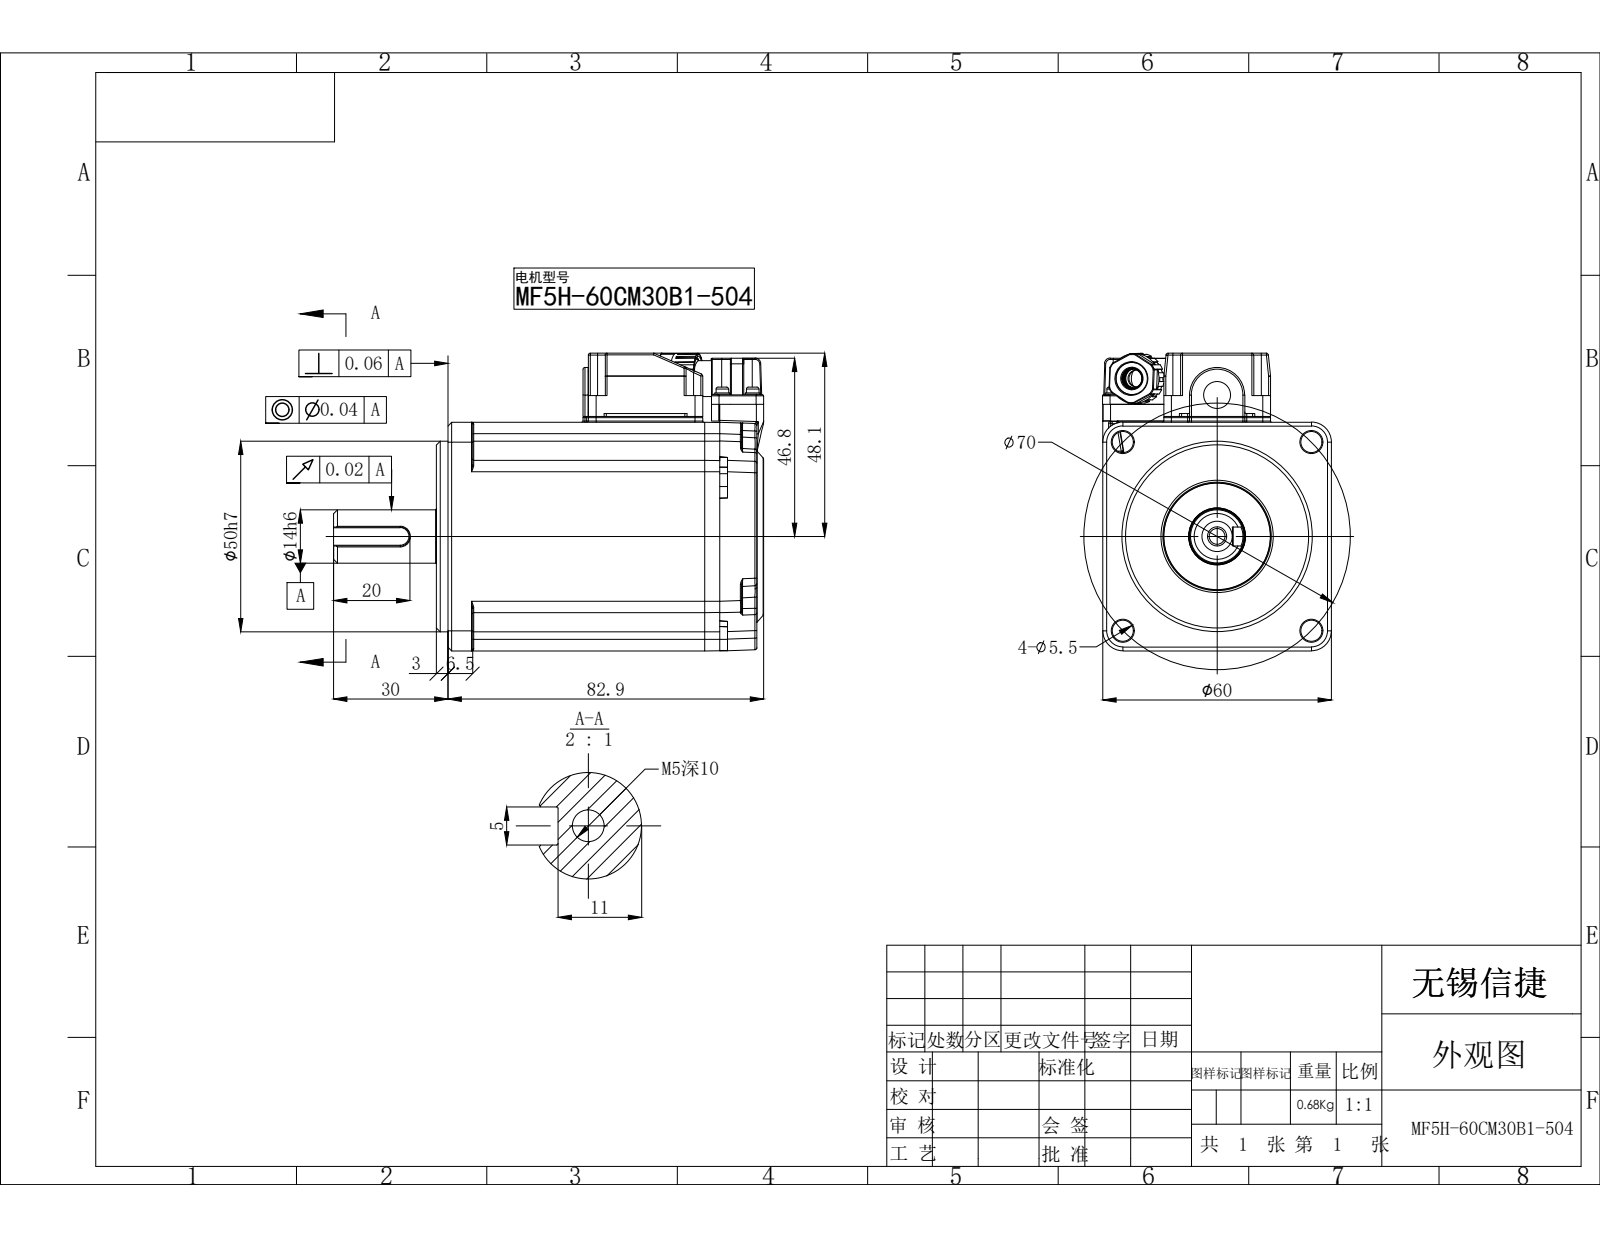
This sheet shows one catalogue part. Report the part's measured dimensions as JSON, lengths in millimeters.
{"part_name": "MF5H-60CS30B1-504", "step_written_by": "SolidWorks 2016 (CONFIG_CONTROL_DESIGN)", "units": "millimeters", "bodies": {"solids": 0, "faces": 917, "planar": 297, "cylindrical": 317, "other": 303}, "overall_size": [112.9, 78.19, 60.19], "round_holes": [[5.5, 5], [2.3, 4], [3.5, 3], [4.2, 1], [5, 1], [6.8, 1], [11.7, 1], [15, 1]], "round_bosses_or_shafts": [[3.9, 4], [3.3, 4], [50, 1], [28, 1], [14, 1], [10.4, 1], [9.4, 1]], "partial_cylinders_radius": [[0.5, 66], [0.3, 52], [2, 20], [3, 17], [0.2, 12], [5, 7], [1.5, 6], [2.25, 4]], "face_to_face_distances": [60, 11.5, 85.9, 74.4, 1.8, 9.7, 3, 82.9, 71.4, 81.1], "hole_center_spacings": [35, 49.5, 8.55, 31.64, 41.31, 52.4, 66.18, 23.6]}
